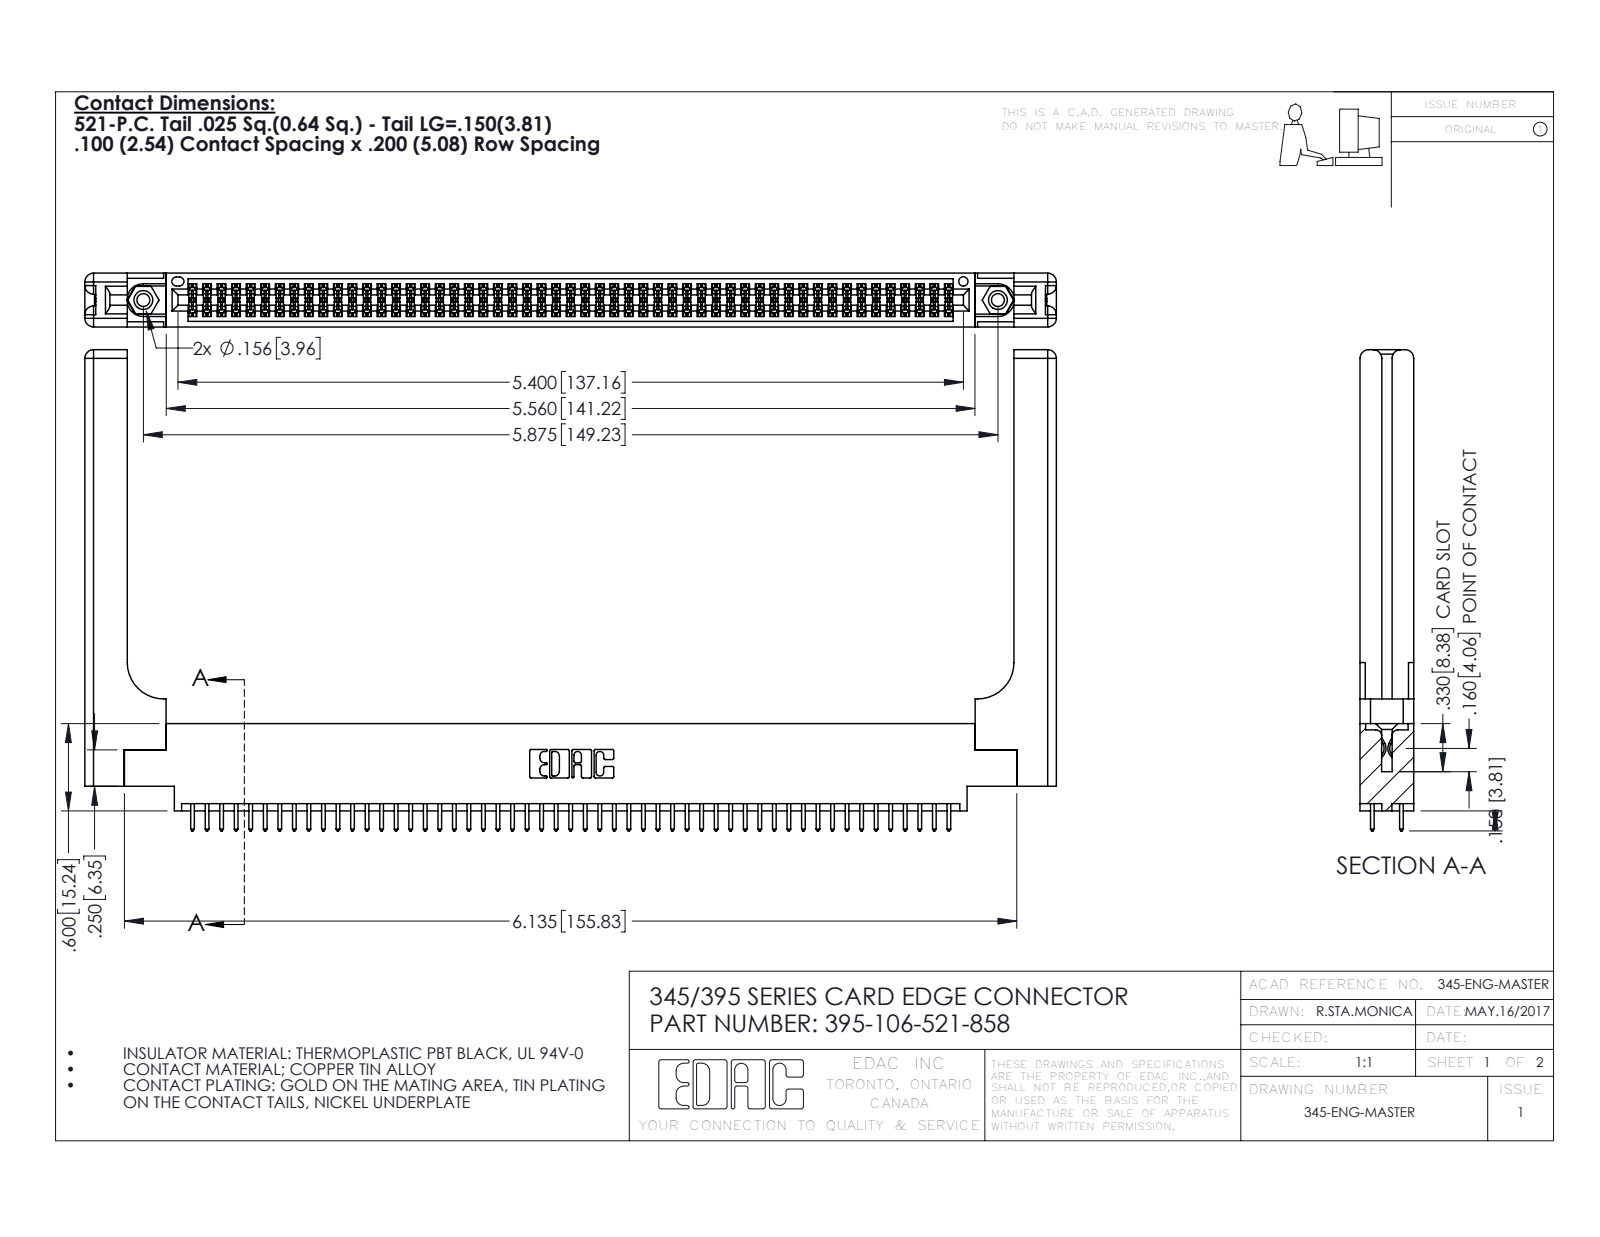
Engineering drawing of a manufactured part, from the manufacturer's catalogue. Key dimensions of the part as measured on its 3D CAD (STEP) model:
Part name (STEP PRODUCT): 345-292-001_345-293-121; 345-250-001_345-250-001-102; 395-106-521-858; 345 Part_0.170 Offset - 0.156 Dia-TH (+1 more)
STEP written by: SolidWorks 2016 (CONFIG_CONTROL_DESIGN)
Units: inches
Bodies: 111 solids, 5686 faces (3730 planar, 1896 cylindrical, 60 other)
Overall size (bounding box): 6.679 × 3.307 × 0.37
Volume: 1.52 in³ · Surface area: 45.59 in²
Round holes (diameter × count): ⌀0.089 ×2, ⌀0.125 ×2, ⌀0.156 ×2, ⌀0.064 ×1
Round bosses / shafts (diameter × count): ⌀0.155 ×2
Partial cylindrical surfaces — rounded edges, fillets, slot ends (radius × count): R0.006 ×159, R0.01 ×106, R0.01 ×22, R0.06 ×16, R0.007 ×6, R0.031 ×6, R0.026 ×3, R0.014 ×2
Main face-to-face distances: 0.072, 0.298, 0.37, 0.098, 0.272, 0.025, 0.2, 0.225, 0.175, 0.148
Hole centre spacings: 0.27, 5.639, 5.875
